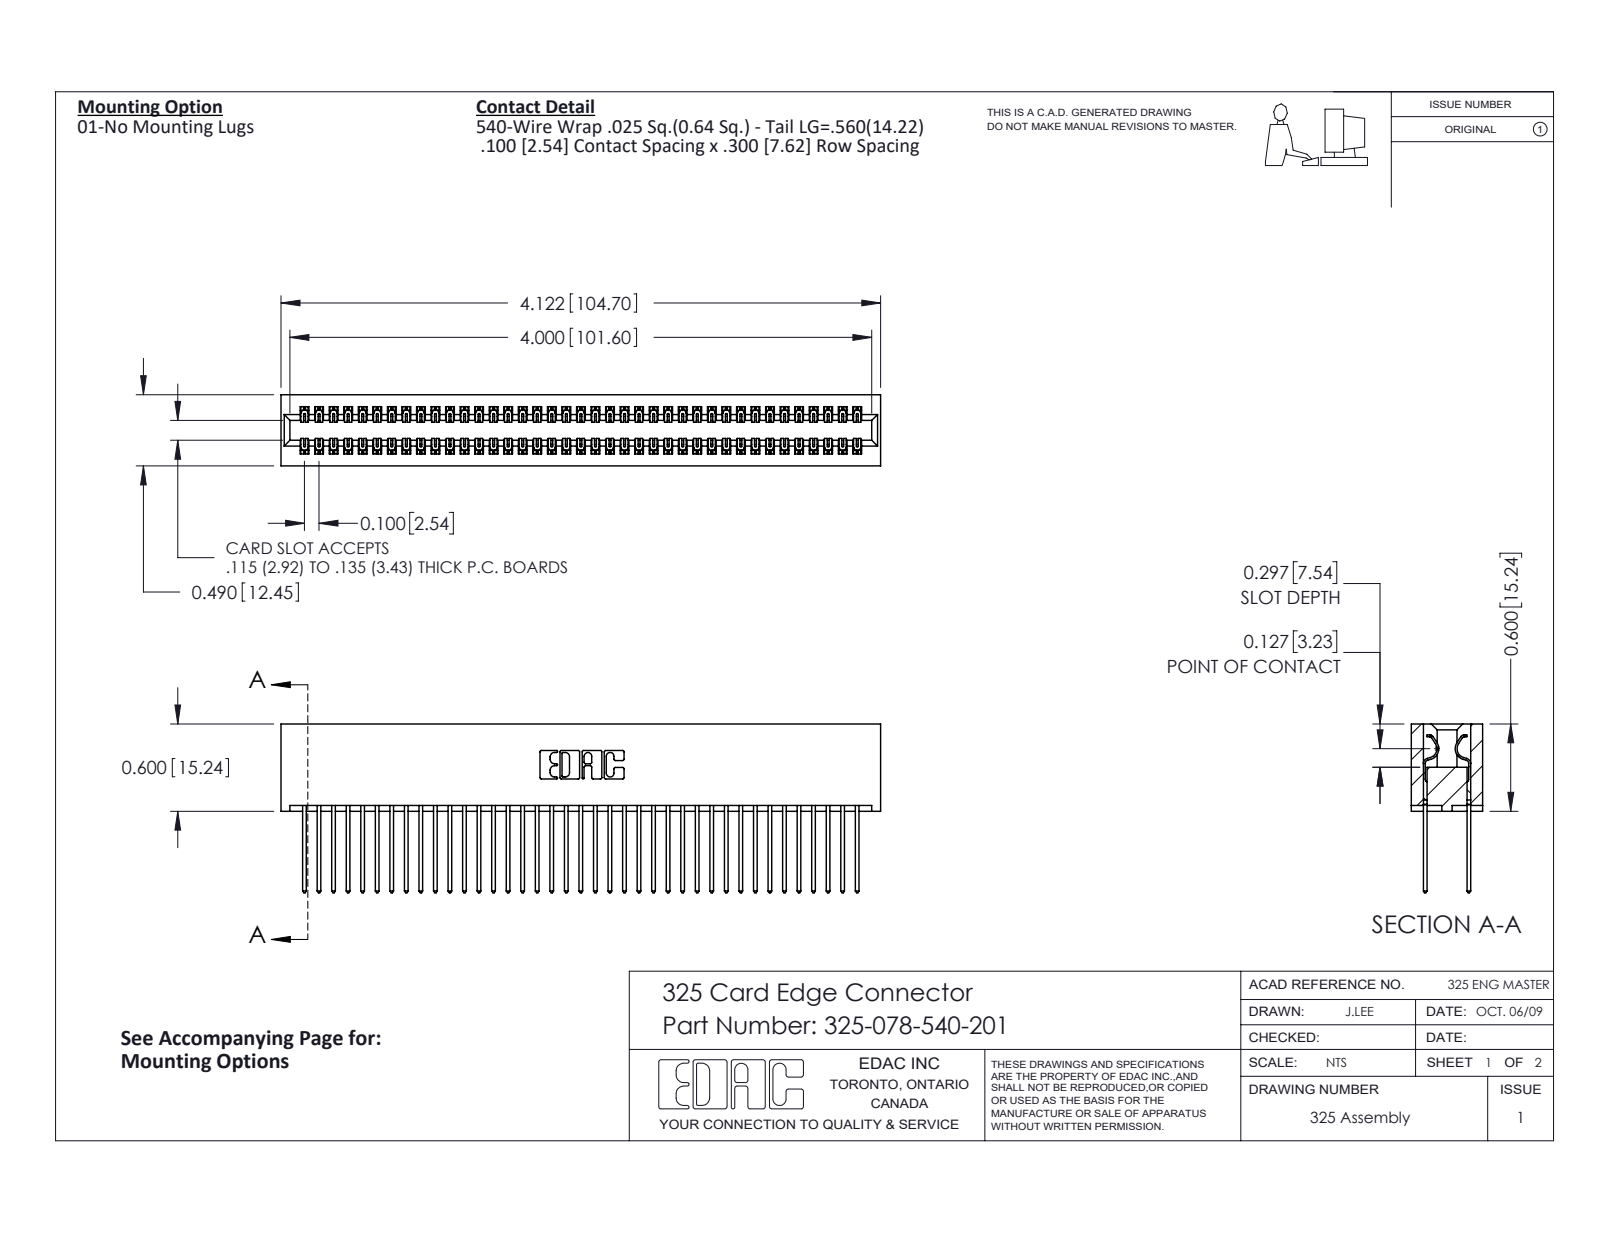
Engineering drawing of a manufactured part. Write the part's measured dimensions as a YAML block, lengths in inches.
part_name: "325-078-540-201; 325-292-001_325-293-140; 325 Part_Lugless"
step_written_by: "SolidWorks 2016 (CONFIG_CONTROL_DESIGN)"
units: inches
bodies: {solids: 79, faces: 4162, planar: 2874, cylindrical: 1288, other: 0}
overall_size: [4.122, 1.16, 0.49]
volume: 0.878
surface_area: 30.1
partial_cylinders:
  - {radius: 0.006, count: 117}
  - {radius: 0.01, count: 78}
  - {radius: 0.01, count: 22}
  - {radius: 0.007, count: 6}
  - {radius: 0.031, count: 6}
  - {radius: 0.026, count: 3}
  - {radius: 0.014, count: 2}
  - {radius: 0.022, count: 2}
face_to_face_distances: [0.083, 0.407, 0.3, 0.107, 0.383, 0.025, 0.325, 0.49, 0.275, 0.56]
